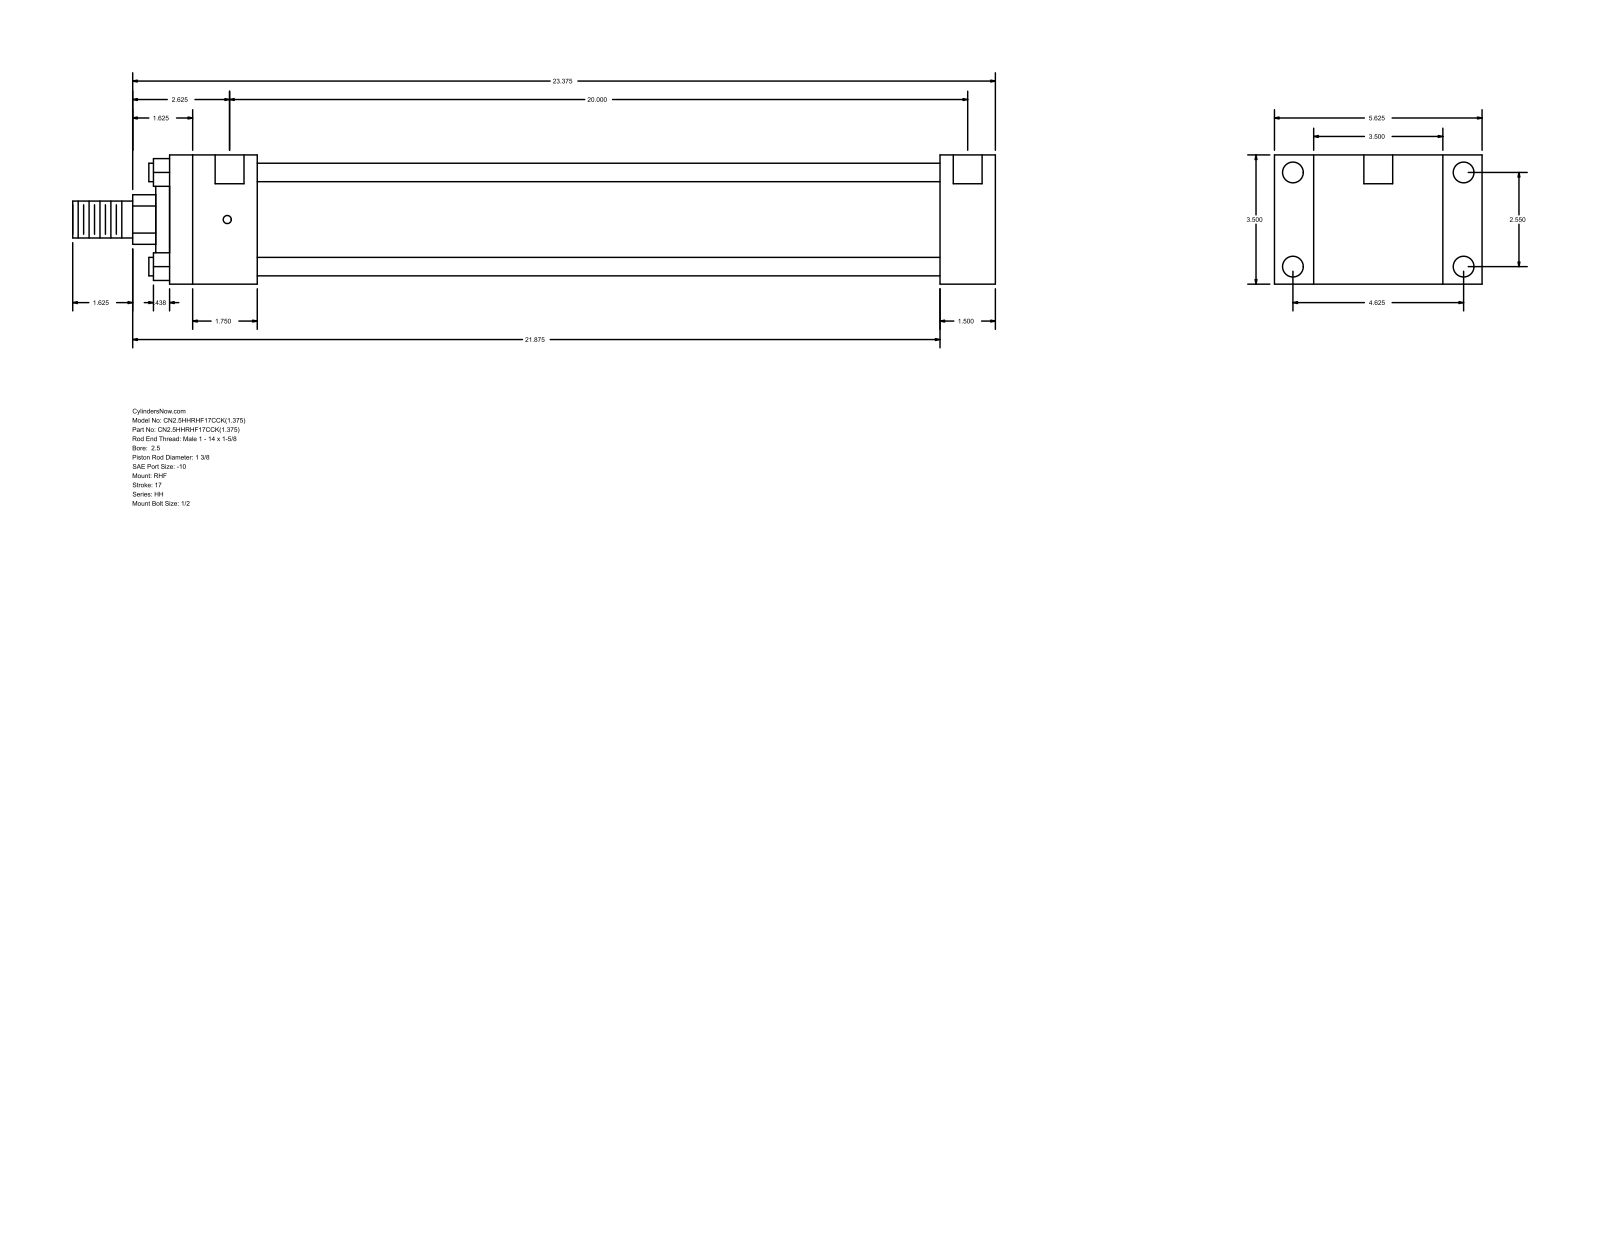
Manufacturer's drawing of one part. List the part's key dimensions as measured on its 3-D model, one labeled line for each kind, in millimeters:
Part name (STEP PRODUCT): HH_RHF__0250_1.375
STEP written by: GSSL Pune (CONFIG_CONTROL_DESIGN)
Units: millimetres
Bodies: 0 solids, 88 faces (60 planar, 28 cylindrical, 0 other)
Overall size (bounding box): 635 × 142.88 × 88.9
Round holes (diameter × count): ⌀5.56 ×4, ⌀14.3 ×4, ⌀19.84 ×2
Round bosses / shafts (diameter × count): ⌀12.7 ×4, ⌀73.03 ×1, ⌀50.8 ×1, ⌀34.92 ×1, ⌀25.4 ×1
Partial cylindrical surfaces — rounded edges, fillets, slot ends (radius × count): R17.06 ×1
Main face-to-face distances: 88.9, 38.11, 26.99, 115.89, 530.22, 568.33, 142.88, 60.32, 469.9, 508.01
Hole centre spacings: 64.76, 117.48, 134.15, 511.17, 1.58, 1.59, 508, 509.58
